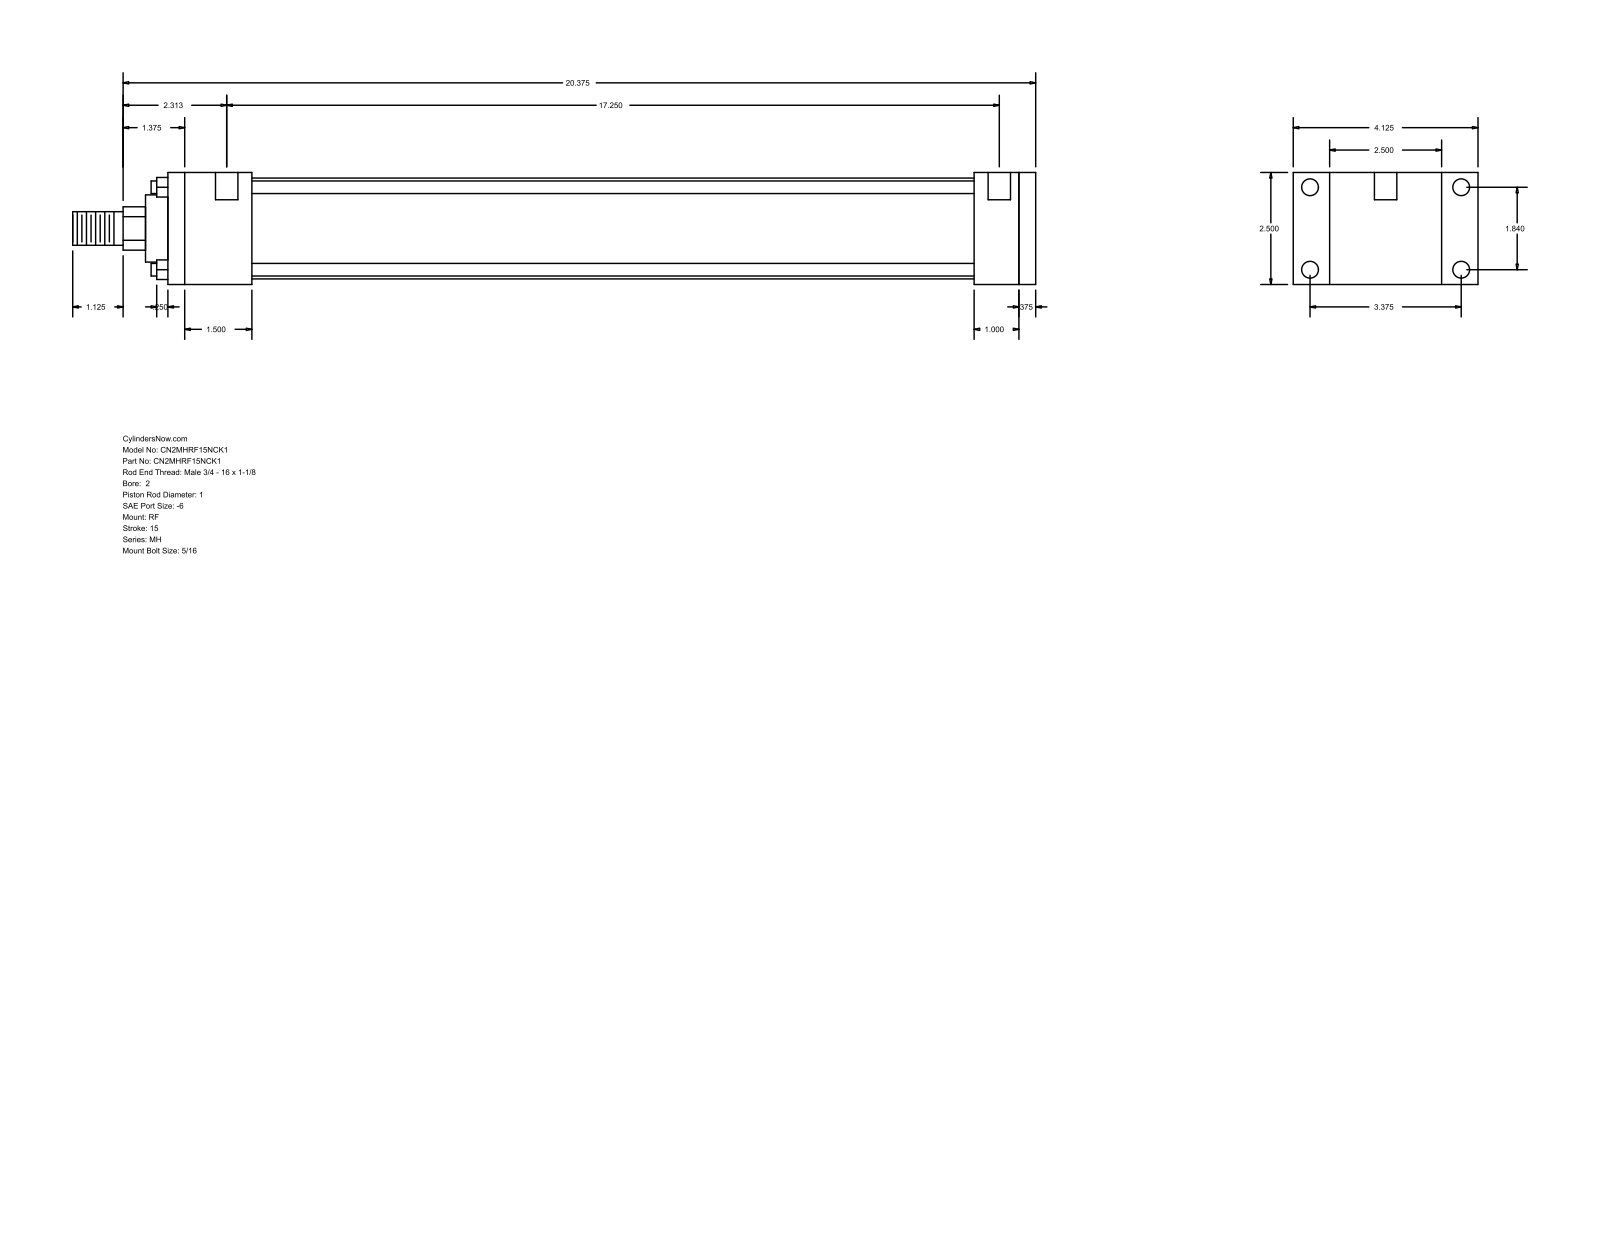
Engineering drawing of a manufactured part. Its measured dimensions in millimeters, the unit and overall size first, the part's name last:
Units: millimetres
Overall size (bounding box): 546.1 × 104.78 × 63.5
Round holes (diameter × count): ⌀5.56 ×4, ⌀9.53 ×4, ⌀12.7 ×2
Round bosses / shafts (diameter × count): ⌀7.14 ×4, ⌀57.15 ×1, ⌀38.1 ×1, ⌀25.4 ×1, ⌀19.05 ×1
Partial cylindrical surfaces — rounded edges, fillets, slot ends (radius × count): R12.29 ×1
Main face-to-face distances: 63.5, 492.12, 9.52, 482.6, 20.64, 25.4, 47.63, 457.2, 409.57, 434.97
Hole centre spacings: 46.74, 85.72, 97.63, 446.08, 3.17, 4.76, 438.15, 441.32
Bodies: 0 solids, 92 faces (64 planar, 28 cylindrical, 0 other)
Part name (STEP PRODUCT): MH_RF__0200_1
STEP written by: GSSL Pune (CONFIG_CONTROL_DESIGN)
